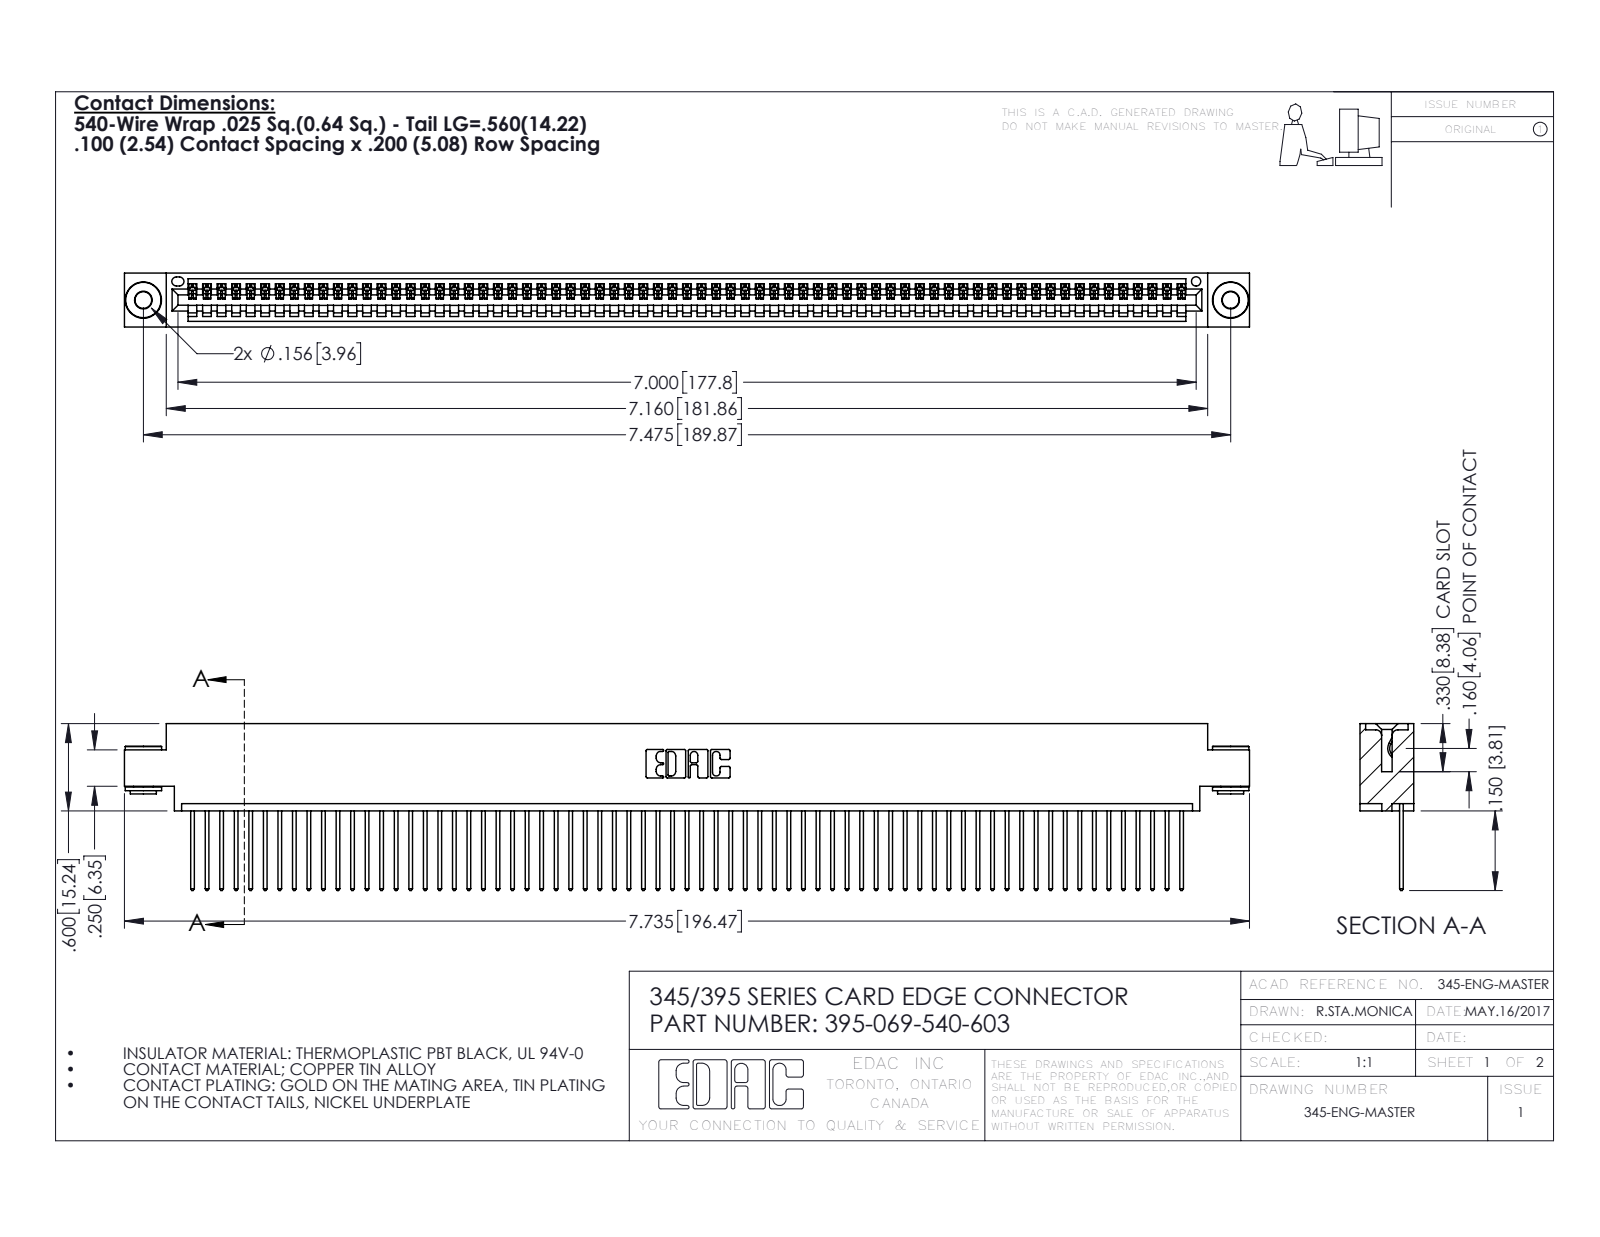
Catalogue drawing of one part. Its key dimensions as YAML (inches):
part_name: "345 Part_0.170 Offset - 0.156 Dia-TH; 395-069-540-603; 345-292-001_345-293-140; 345-250-002_345-250-002-102"
step_written_by: "SolidWorks 2016 (CONFIG_CONTROL_DESIGN)"
units: inches
bodies: {solids: 72, faces: 4170, planar: 2854, cylindrical: 1308, other: 8}
overall_size: [7.735, 1.147, 0.37]
volume: 1.152
surface_area: 41.03
round_holes:
  - {diameter: 0.116, count: 2}
  - {diameter: 0.156, count: 2}
  - {diameter: 0.064, count: 1}
round_bosses_or_shafts:
  - {diameter: 0.25, count: 2}
  - {diameter: 0.18, count: 2}
  - {diameter: 0.136, count: 2}
partial_cylinders:
  - {radius: 0.006, count: 138}
  - {radius: 0.01, count: 138}
  - {radius: 0.01, count: 22}
  - {radius: 0.007, count: 6}
  - {radius: 0.031, count: 6}
  - {radius: 0.026, count: 3}
  - {radius: 0.031, count: 2}
  - {radius: 0.04, count: 2}
face_to_face_distances: [0.072, 0.298, 0.37, 0.098, 0.272, 0.025, 0.2, 0.225, 0.175, 0.149]
hole_center_spacings: [0.27, 7.239, 7.475]
